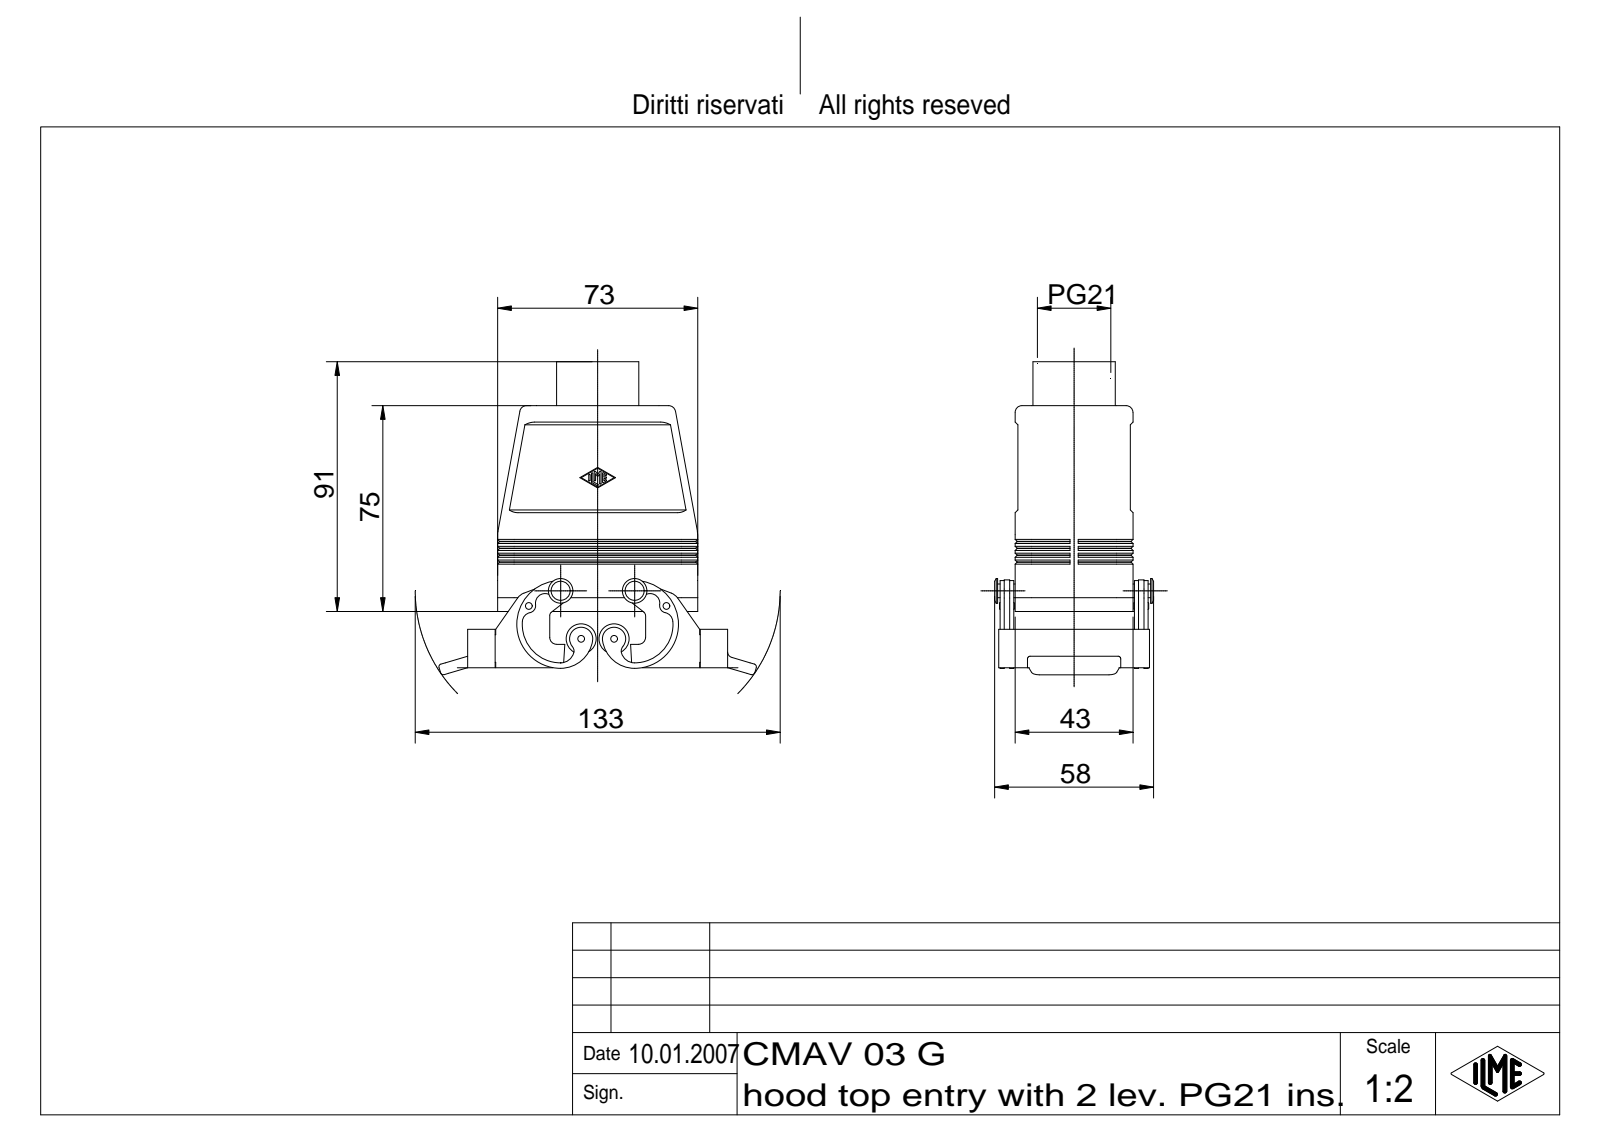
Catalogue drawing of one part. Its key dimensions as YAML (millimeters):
part_name: "CAV Tüllengehäuse 2 Bügel für einen Einsatz"
step_written_by: "Autodesk Inventor 7 (AUTOMOTIVE_DESIGN)"
units: millimeters
bodies: {solids: 1, faces: 849, planar: 258, cylindrical: 230, other: 361}
overall_size: [115.79, 114.08, 58]
volume: 89235
surface_area: 53708
round_holes:
  - {diameter: 2.5, count: 2}
  - {diameter: 24.78, count: 1}
  - {diameter: 26.78, count: 1}
round_bosses_or_shafts:
  - {diameter: 11, count: 2}
  - {diameter: 9, count: 2}
  - {diameter: 5, count: 2}
  - {diameter: 2, count: 2}
  - {diameter: 30, count: 1}
  - {diameter: 25.78, count: 1}
partial_cylinders:
  - {radius: 0.25, count: 14}
  - {radius: 1, count: 12}
  - {radius: 2.5, count: 10}
  - {radius: 6, count: 10}
  - {radius: 3, count: 8}
  - {radius: 2, count: 7}
  - {radius: 3.5, count: 4}
  - {radius: 5, count: 4}
face_to_face_distances: [4, 3, 39, 1, 38, 35, 42, 43, 41, 2]
hole_center_spacings: [50.2]
